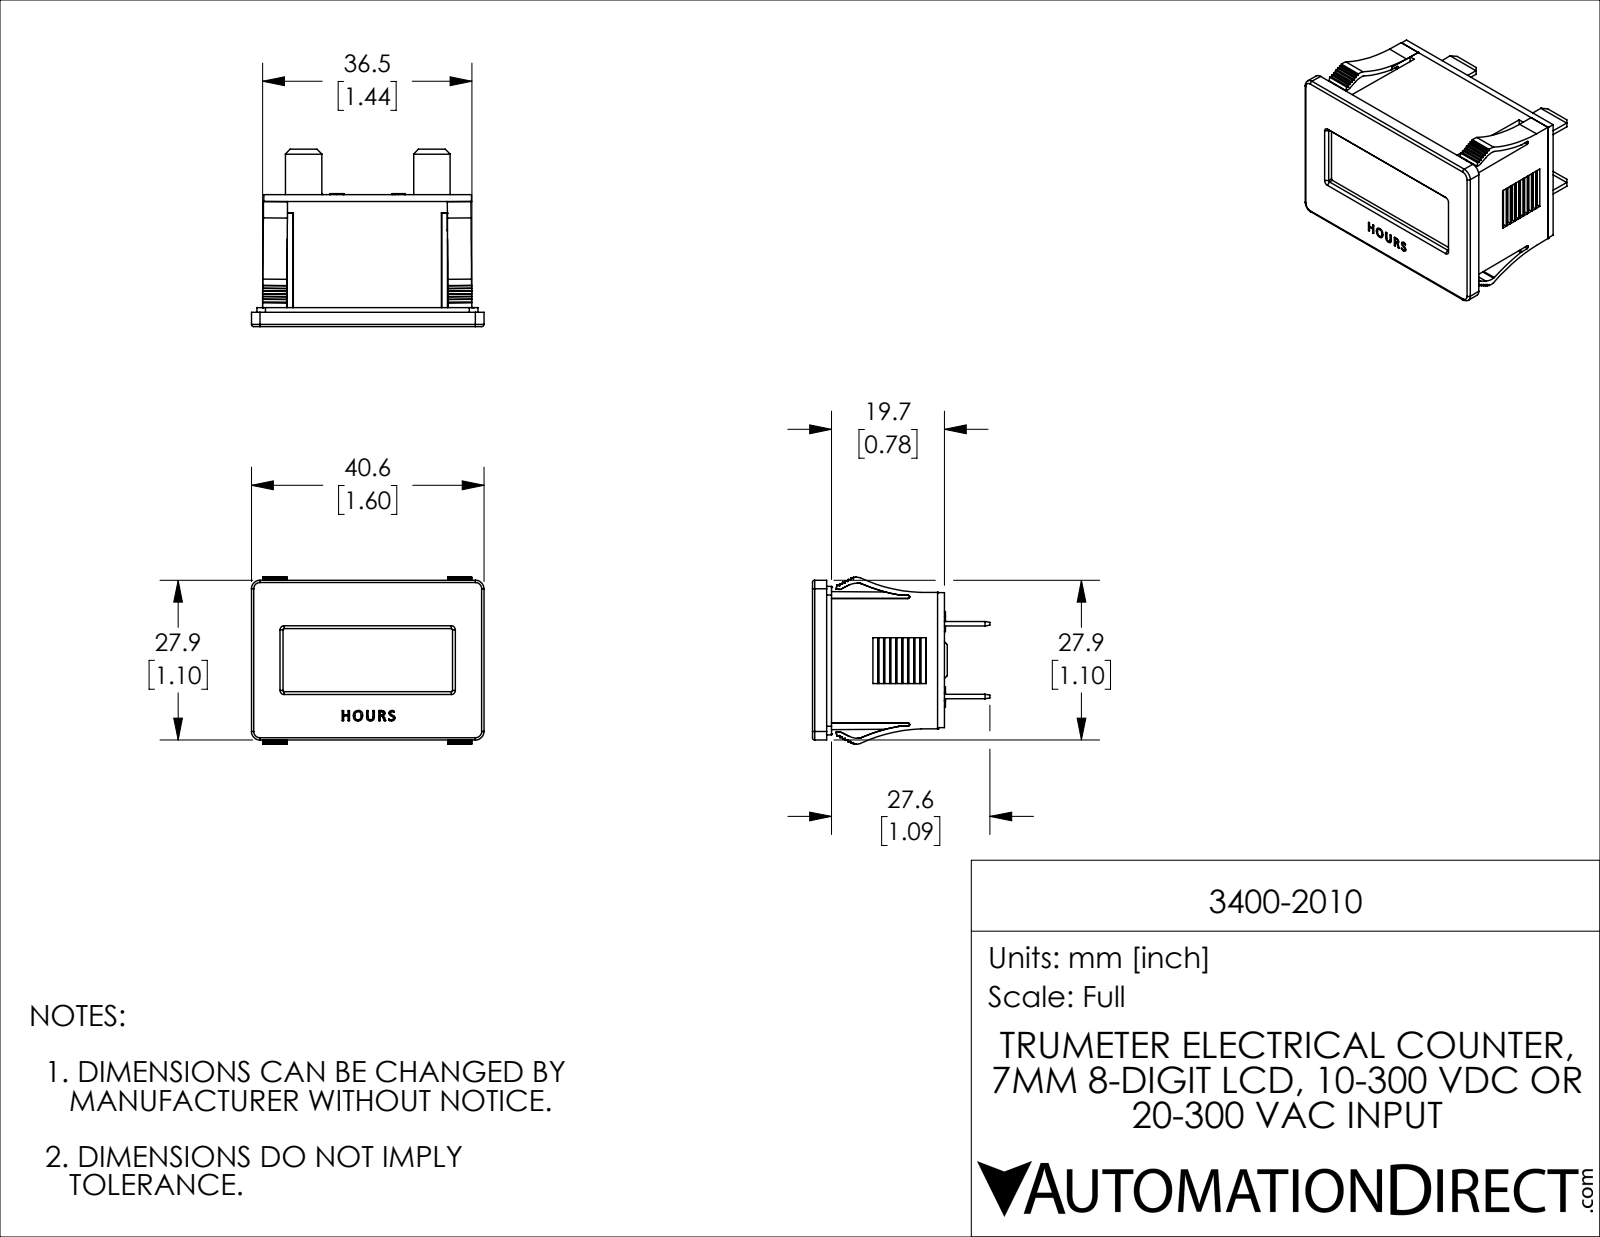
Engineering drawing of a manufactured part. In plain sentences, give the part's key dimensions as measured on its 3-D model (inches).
The part is named "3400-2010". Its 3-D file was written by "SolidWorks 2021 (CONFIG_CONTROL_DESIGN)". It is 1 solid with 722 faces: 496 planar, 78 cylindrical and 148 other. Overall it measures 1.598 by 1.22 by 1.148 inches. Its volume is 1.234 cubic inches and its surface area 12.16 square inches. Partial cylindrical surfaces (rounded edges, fillets, slot ends): 8 of radius 0.059, 6 of radius 0.01, 4 of radius 0.008, 4 of radius 0.016, 4 of radius 0.03, 2 of radius 0.006, 2 of radius 0.01, 2 of radius 0.015. The main face-to-face distances are 0.047, 0.86, 0.907, 0.048, 0.859, 0.031, 0.811, 0.813, 0.5, 0.828.
